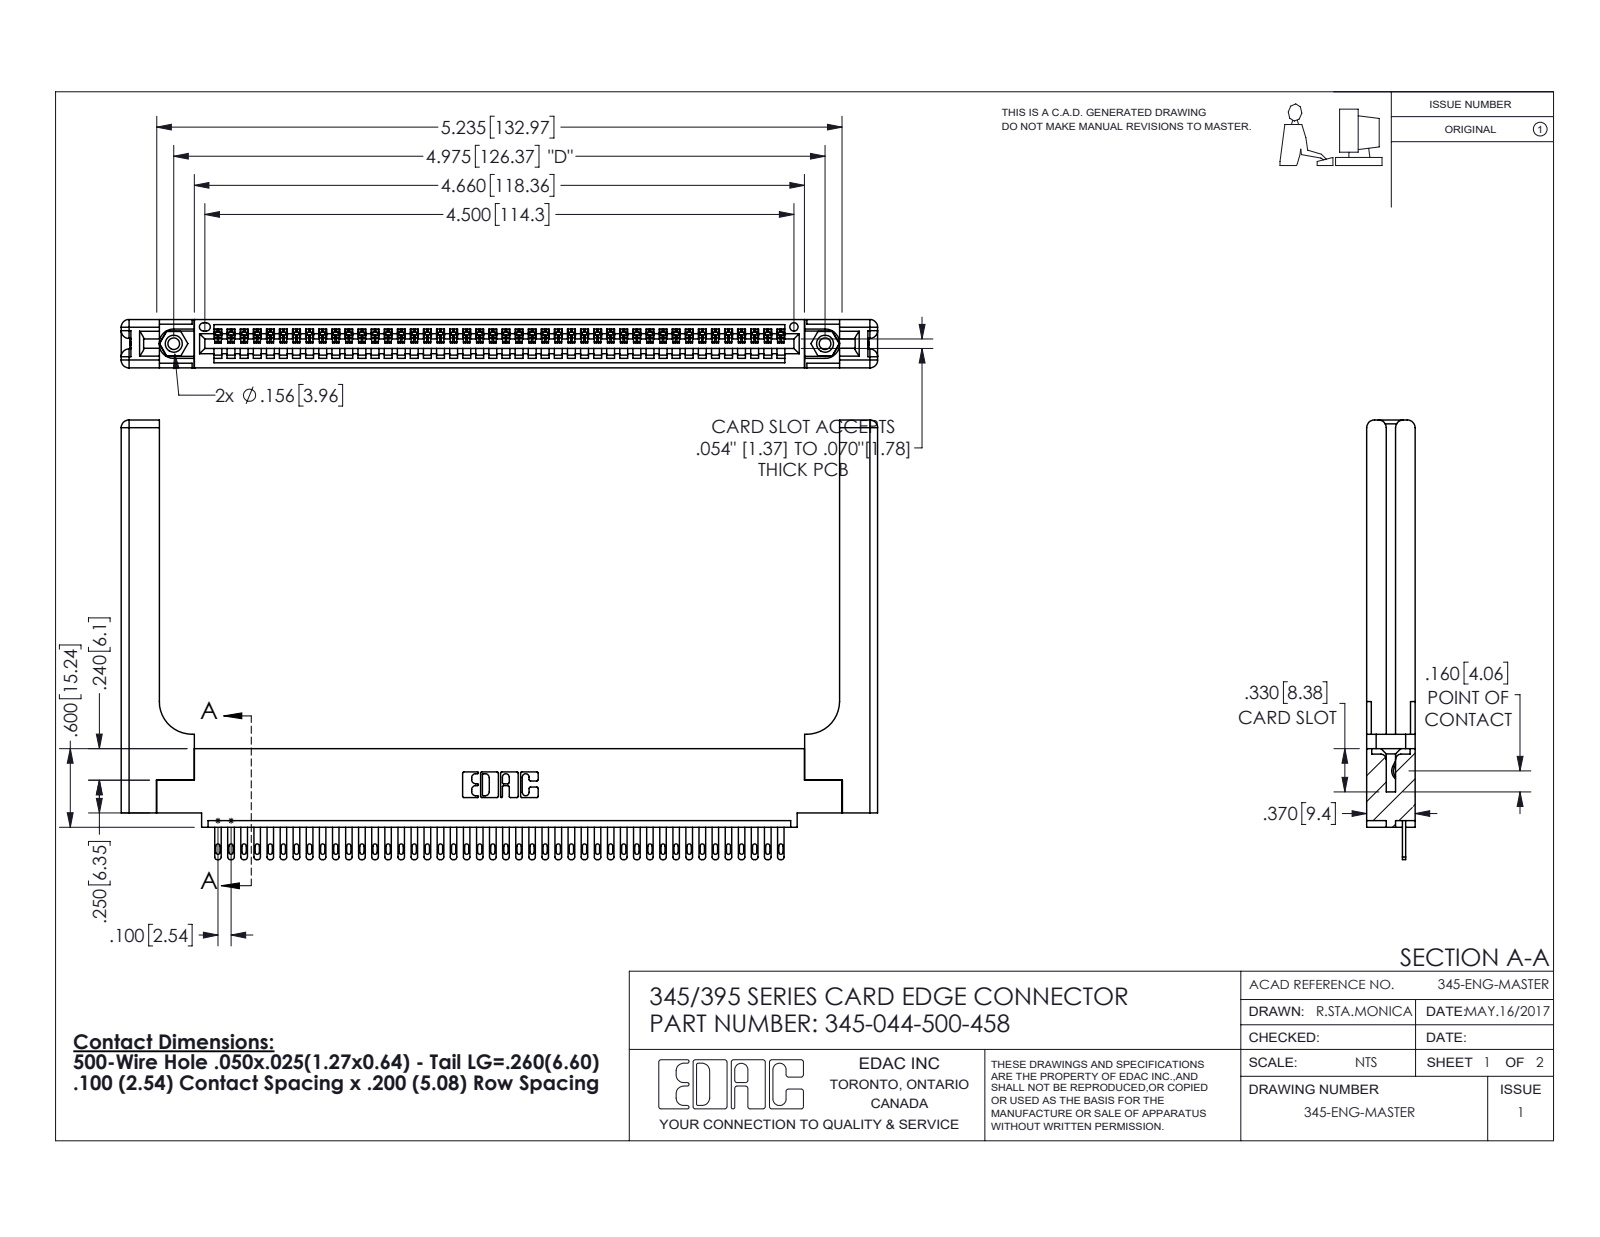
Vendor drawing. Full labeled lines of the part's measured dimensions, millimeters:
Part name (STEP PRODUCT): 345-292-001_345-293-100; 345-044-500-458; 345 Part_0.110 Offset - 0.156 Dia-TH; 345-220-058_345-220-058 (+1 more)
STEP written by: SolidWorks 2016 (CONFIG_CONTROL_DESIGN)
Units: millimetres
Bodies: 49 solids, 2762 faces (1728 planar, 974 cylindrical, 60 other)
Overall size (bounding box): 146.8 × 85.3 × 9.4
Volume: 22 420 mm³ · Surface area: 24 000 mm²
Round holes (diameter × count): ⌀2.3 ×2, ⌀3.2 ×2, ⌀4 ×2, ⌀1.6 ×1
Round bosses / shafts (diameter × count): ⌀3.9 ×2
Partial cylindrical surfaces — rounded edges, fillets, slot ends (radius × count): R0.2 ×88, R0.4 ×88, R0.5 ×88, R0.3 ×22, R1.5 ×16, R0.2 ×6, R0.8 ×6, R0.7 ×3
Main face-to-face distances: 1.8, 9.4, 7.6, 2.5, 6.9, 0.6, 5.1, 5.7, 3.8, 3.8
Hole centre spacings: 6.9, 120.4, 126.4
